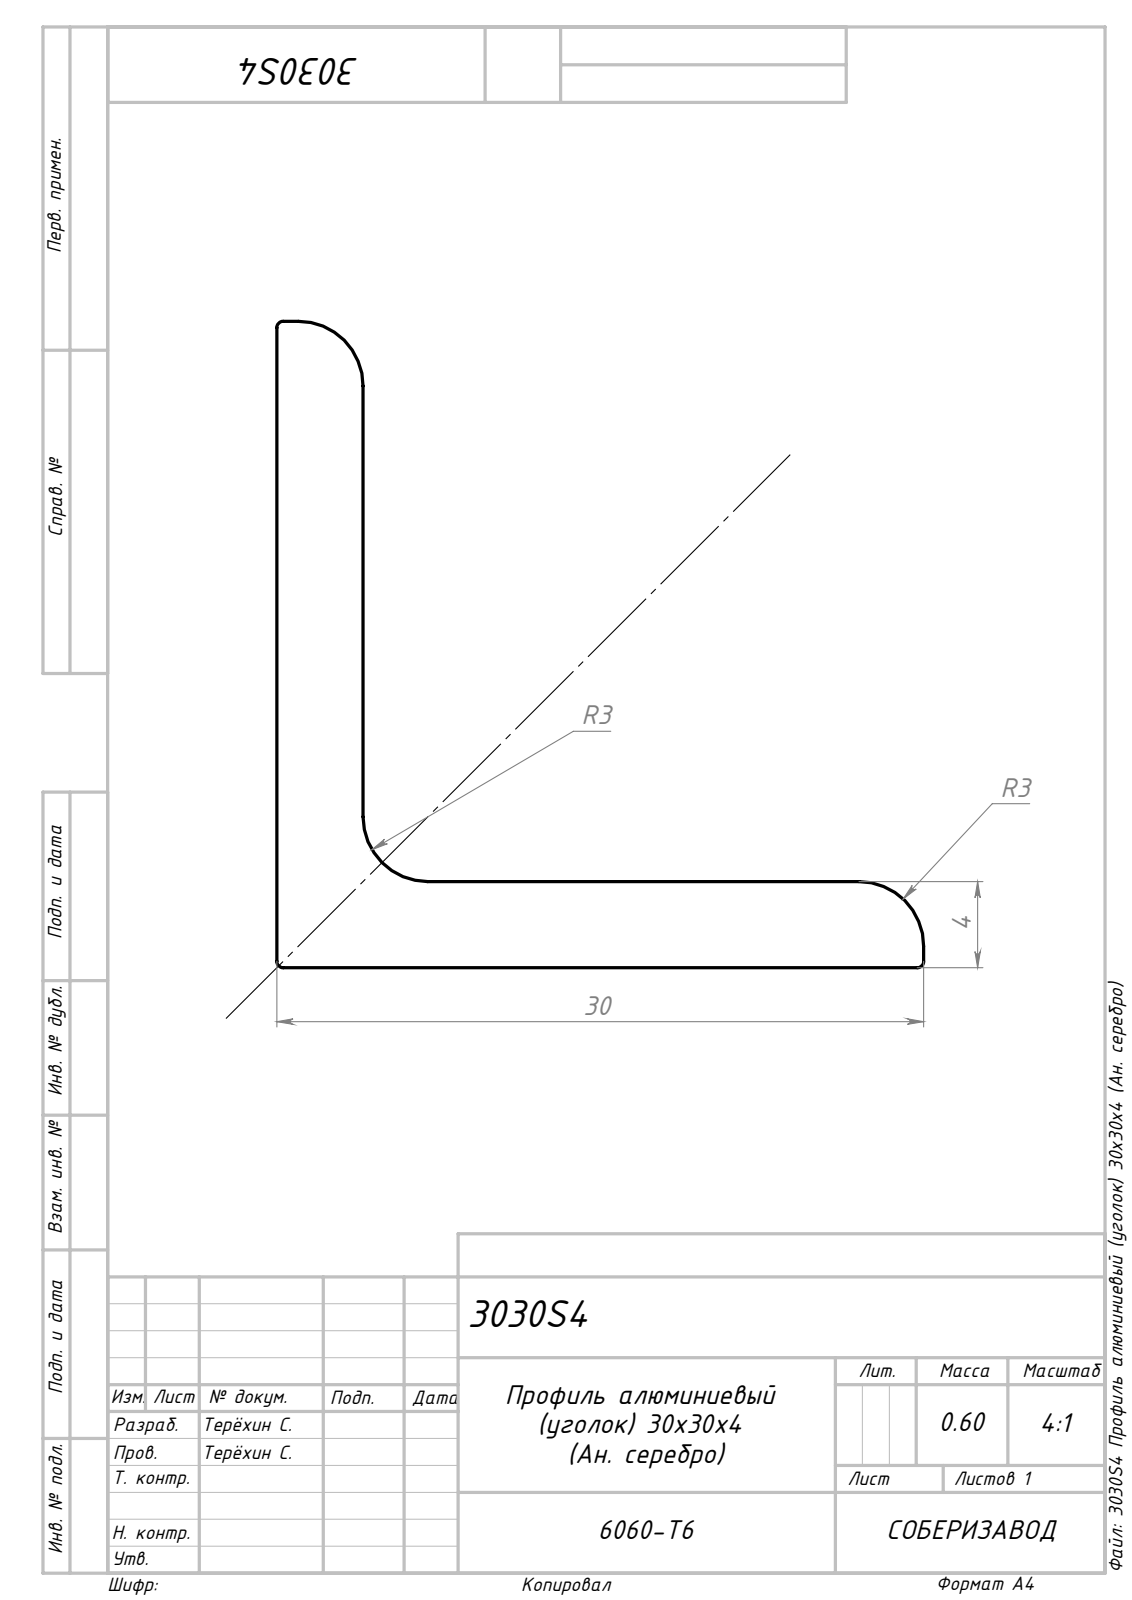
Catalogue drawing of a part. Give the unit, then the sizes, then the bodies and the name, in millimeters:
Units: millimetres
Overall size (bounding box): 1000 × 35 × 35
Partial cylindrical surfaces — rounded edges, fillets, slot ends (radius × count): R0.3 ×3, R3 ×3
Main face-to-face distances: 4, 35, 31, 1000
Volume: 262 011 mm³ · Surface area: 136 275 mm²
Bodies: 1 solid, 14 faces (8 planar, 6 cylindrical, 0 other)
Part name (STEP PRODUCT): 3030S4 Профиль алюминиевый (уголок) 30х30х4 (Ан. серебро)
STEP written by: SolidWorks 2022 (AUTOMOTIVE_DESIGN)
